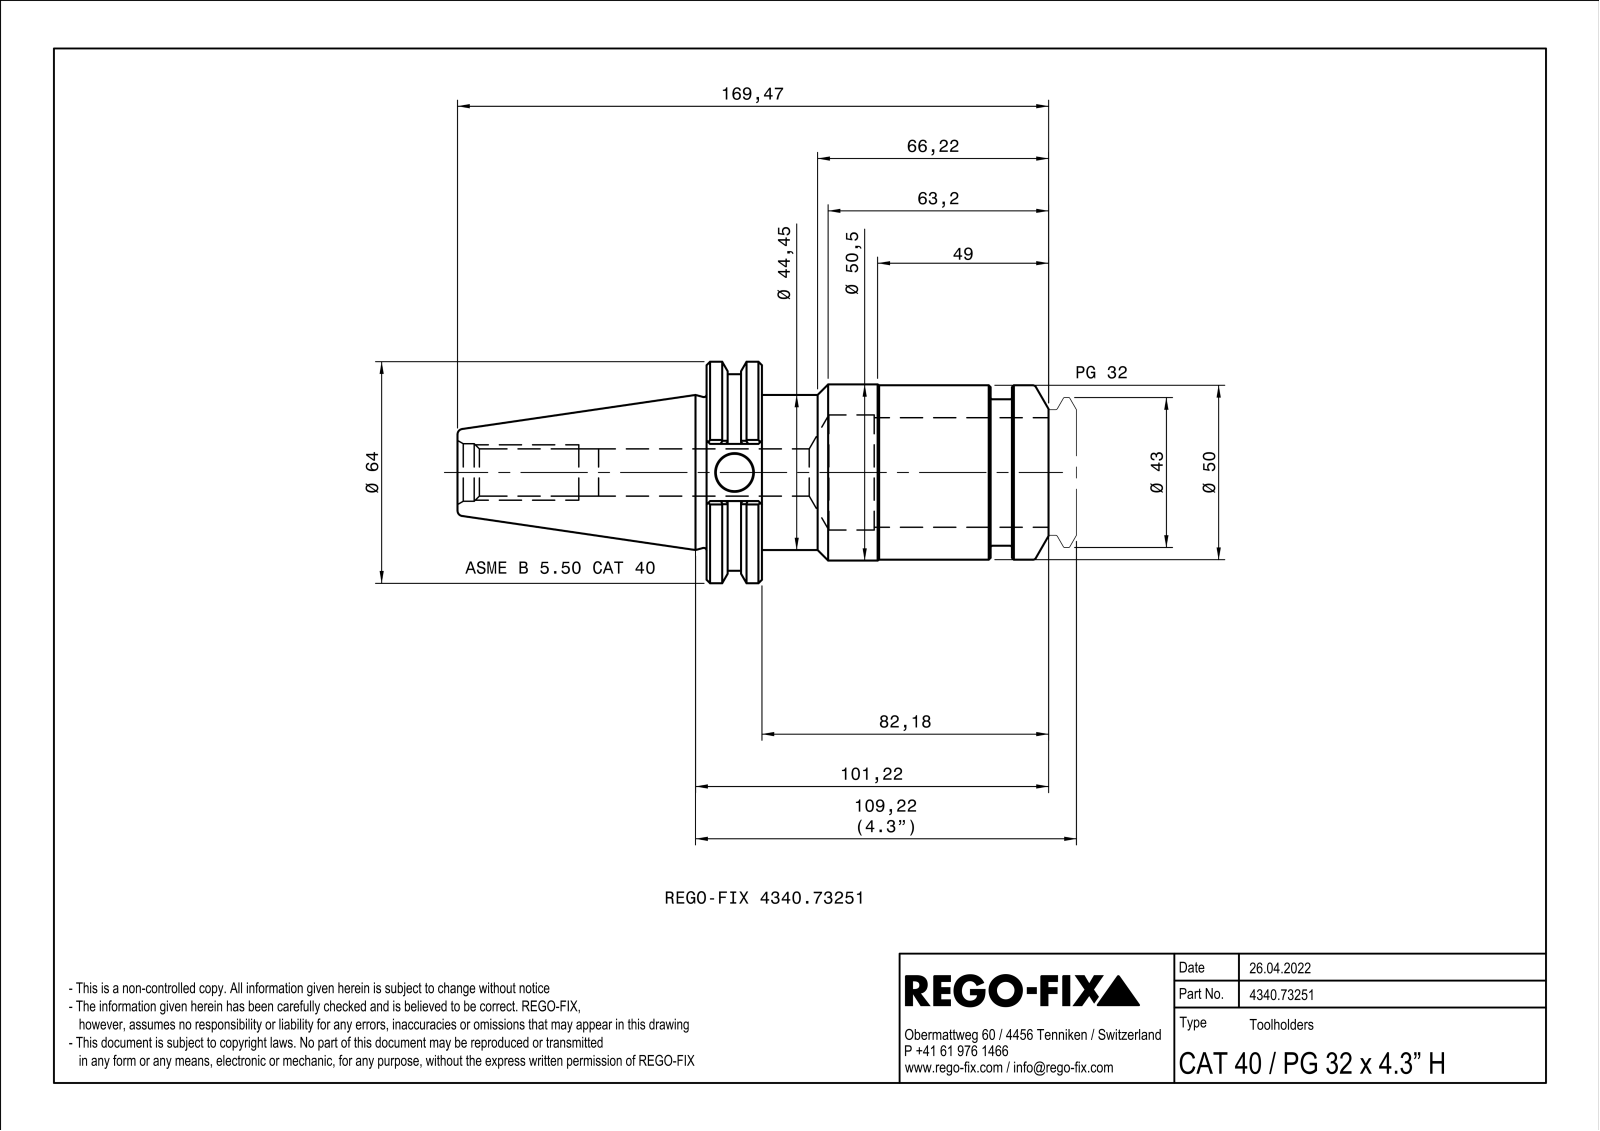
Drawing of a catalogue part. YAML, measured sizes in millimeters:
part_name: "NOCUT"
step_written_by: "SIEMENS PLM Software Solid Edge ST10 (AUTOMOTIVE_DESIGN)"
units: millimeters
bodies: {solids: 1, faces: 102, planar: 33, cylindrical: 22, other: 47}
overall_size: [169.47, 63.5, 60.79]
volume: 193949
surface_area: 40921
round_holes:
  - {diameter: 10.7, count: 1}
  - {diameter: 13.53, count: 1}
  - {diameter: 16.5, count: 1}
  - {diameter: 33, count: 1}
round_bosses_or_shafts:
  - {diameter: 63.5, count: 1}
  - {diameter: 56.36, count: 1}
  - {diameter: 50.5, count: 1}
  - {diameter: 50, count: 1}
  - {diameter: 44.45, count: 1}
  - {diameter: 42, count: 1}
partial_cylinders:
  - {radius: 0.5, count: 4}
face_to_face_distances: [15.87, 65.58, 81.45, 6.1, 71.68, 87.55, 10.5, 16.6, 82.18, 98.05]
